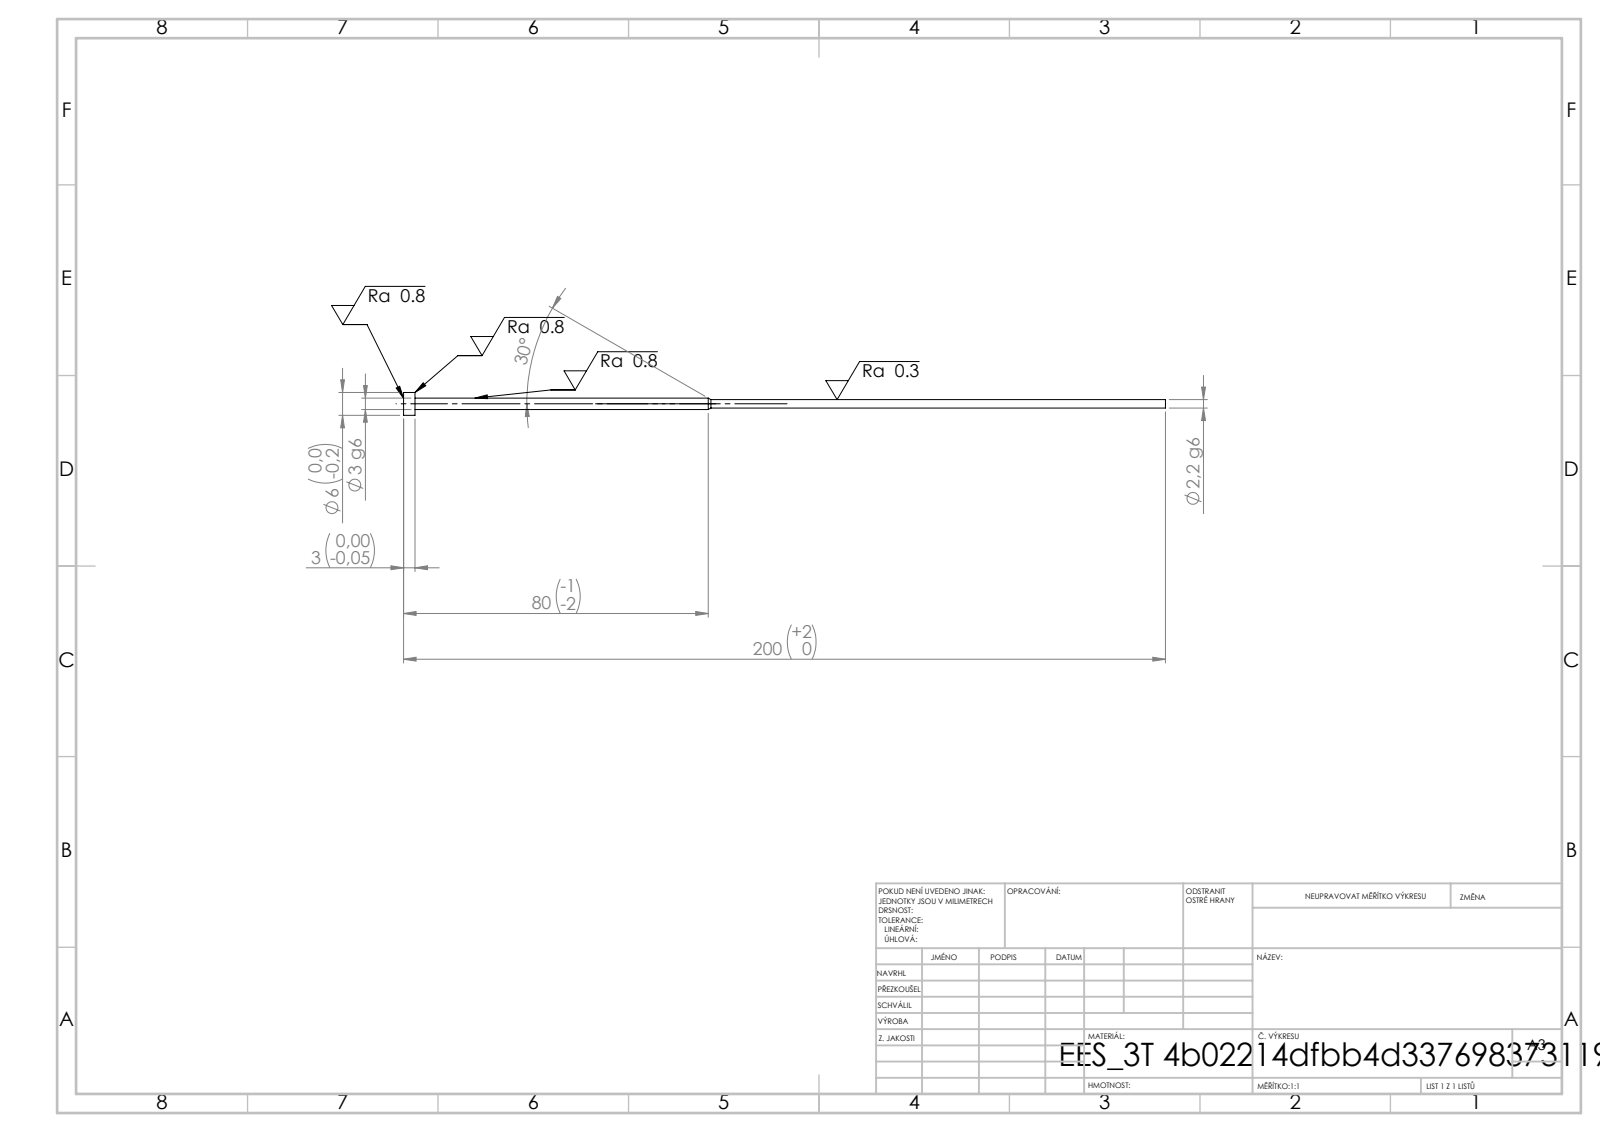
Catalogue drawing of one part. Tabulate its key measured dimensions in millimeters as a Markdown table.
| quantity | value |
| --- | --- |
| STEP written by | SolidWorks 2019 (CONFIG_CONTROL_DESIGN) |
| units | millimeters |
| bodies | 1 solid, 11 faces (3 planar, 6 cylindrical, 2 other) |
| overall size | 200 × 6 × 6 |
| volume | 1 086 mm³ |
| surface area | 1 667 mm² |
| round bosses / shafts (diameter × count) | 6 × 1, 3 × 1, 2.2 × 1 |
| main face-to-face distances | 3, 197, 200 |
